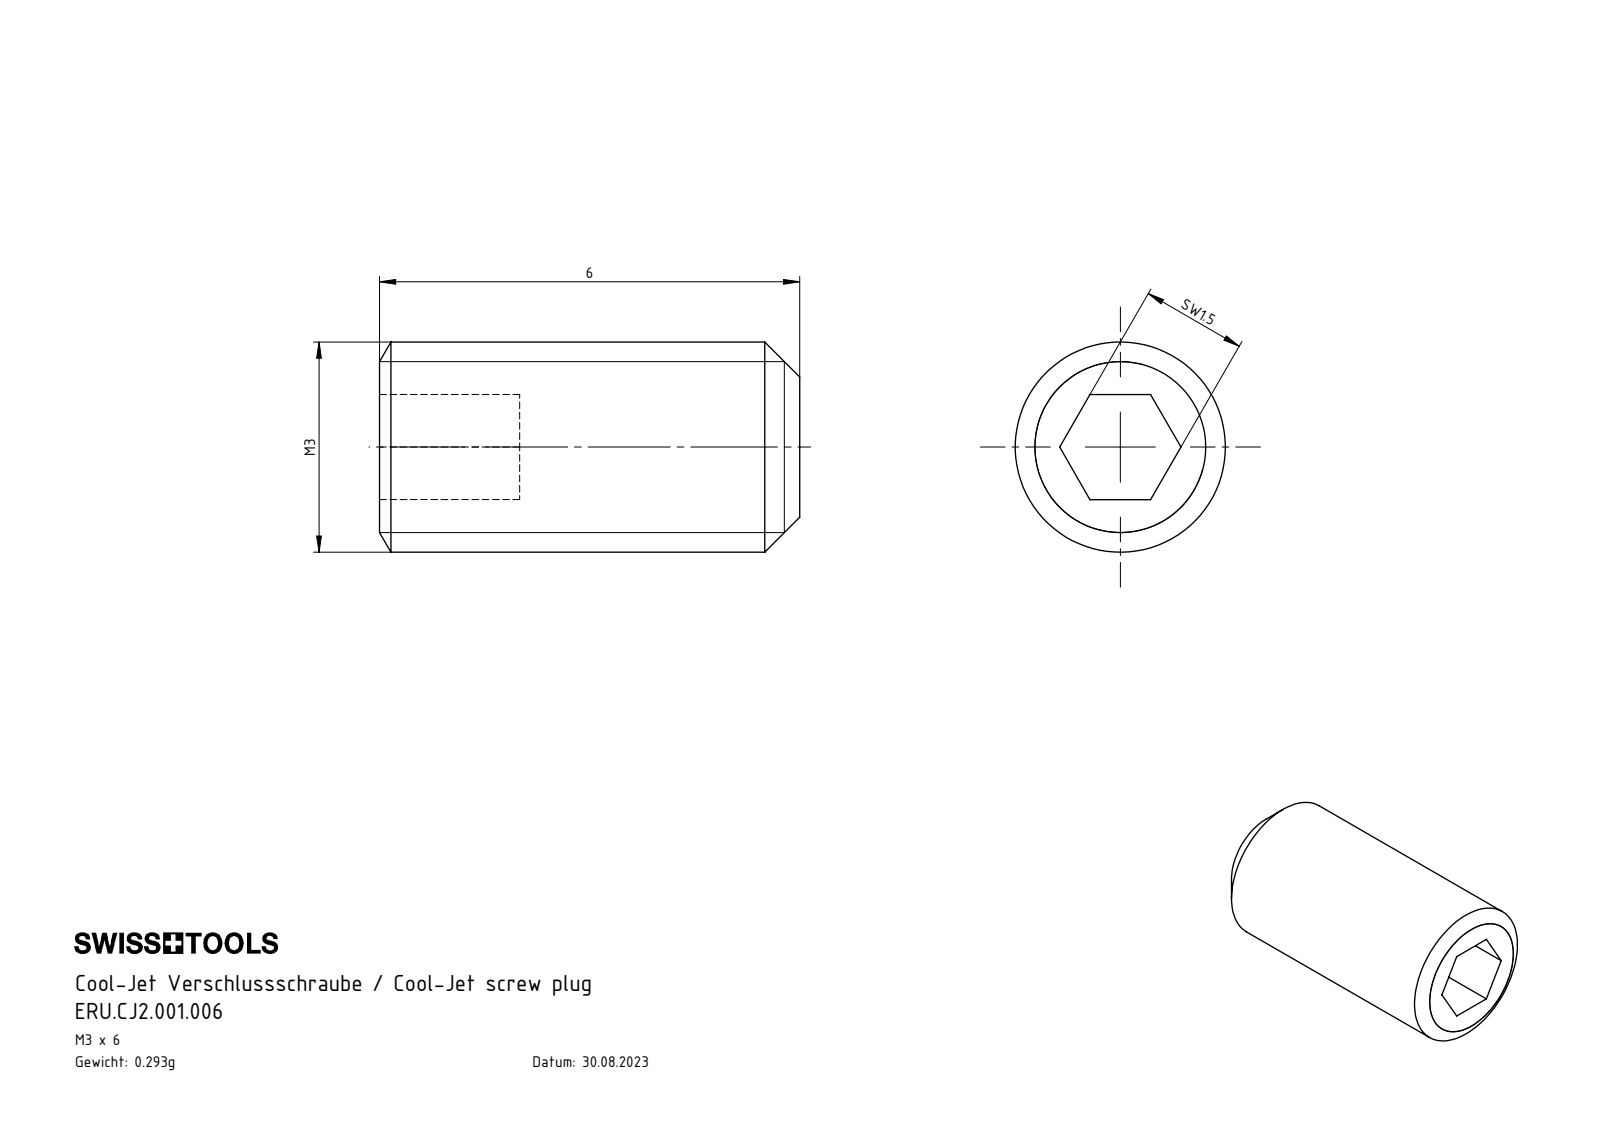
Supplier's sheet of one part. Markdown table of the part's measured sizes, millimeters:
| quantity | value |
| --- | --- |
| part name | ERU.CJ2.001.006 |
| STEP written by | SolidWorks 2017 (AUTOMOTIVE_DESIGN) |
| units | millimeters |
| bodies | 1 solid, 15 faces (9 planar, 2 cylindrical, 4 other) |
| overall size | 6 × 3 × 3 |
| volume | 37 mm³ |
| surface area | 77 mm² |
| round bosses / shafts (diameter × count) | 3 × 1 |
| main face-to-face distances | 1.5, 6, 2, 4 |
